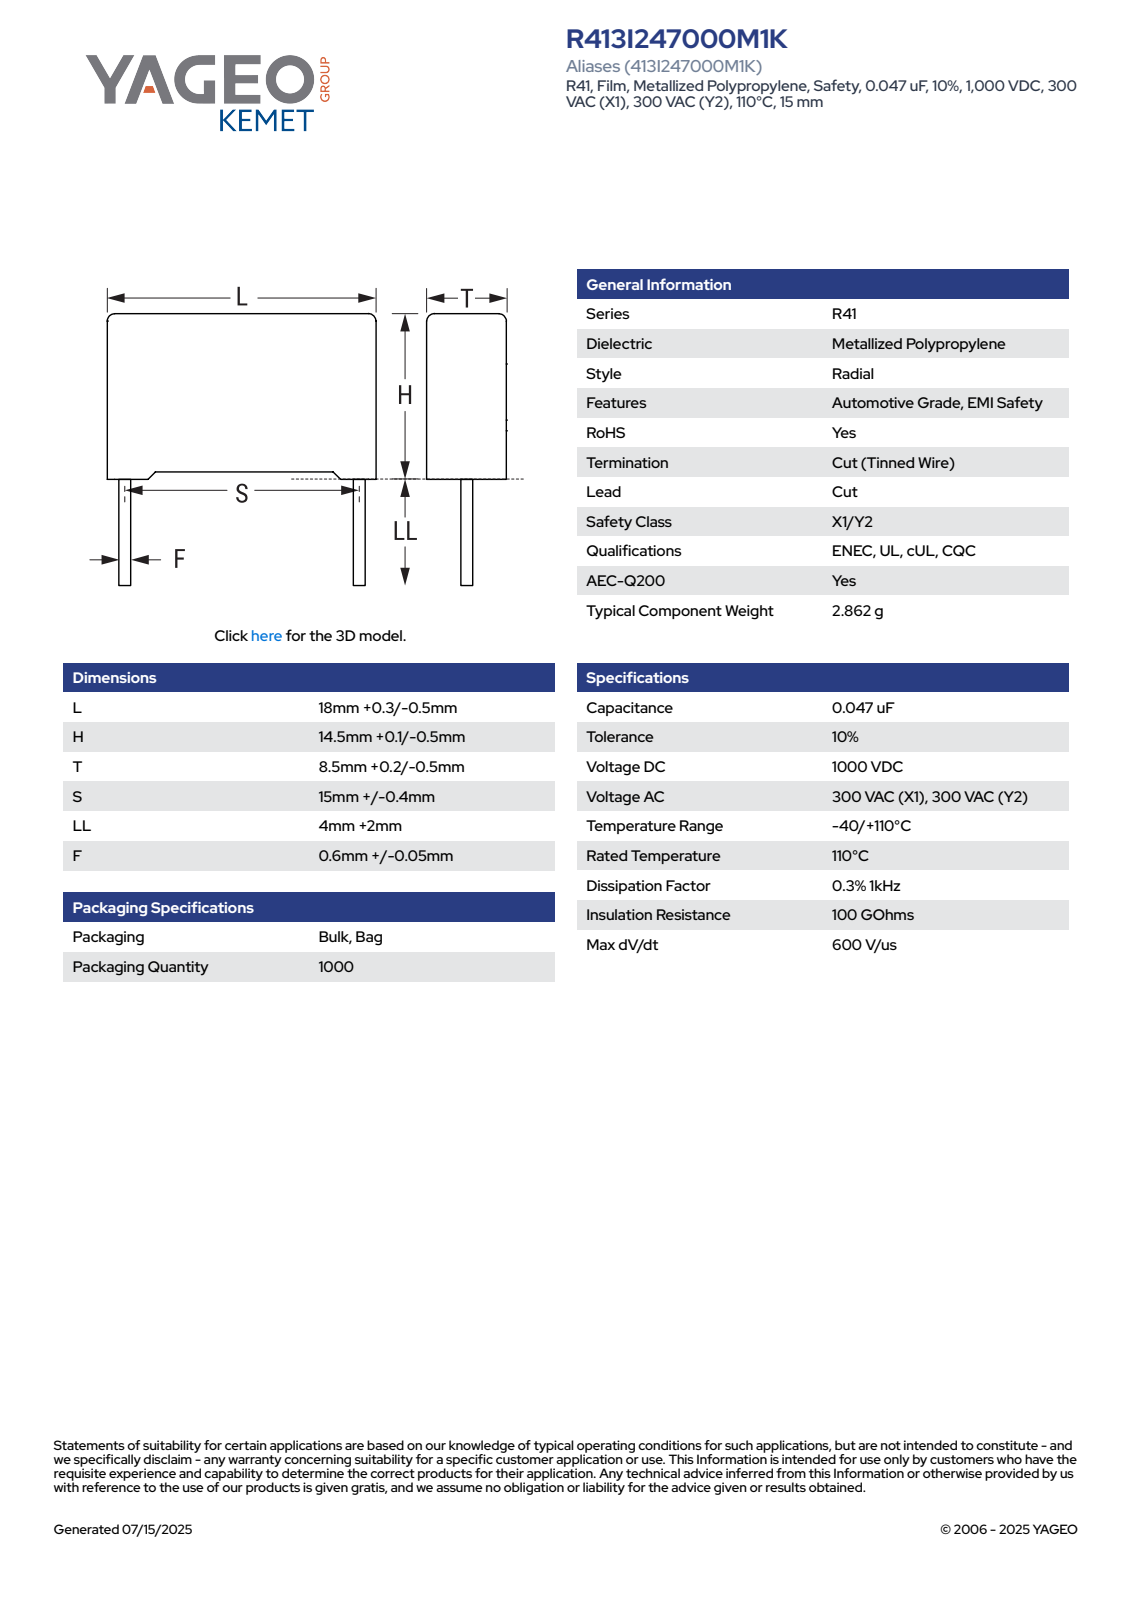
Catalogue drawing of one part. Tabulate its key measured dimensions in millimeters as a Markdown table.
| quantity | value |
| --- | --- |
| part name | CFR_RB2_18X14.5X8.5_L18.3H14.6T8.7S15LL6F0.65 |
| STEP written by | SolidWorks 2021 (AUTOMOTIVE_DESIGN) |
| units | millimeters |
| bodies | 4 solids, 85 faces (77 planar, 8 cylindrical, 0 other) |
| overall size | 20.6 × 18.3 × 8.71 |
| volume | 2 223 mm³ |
| surface area | 1 162 mm² |
| round bosses / shafts (diameter × count) | 0.65 × 2 |
| partial cylindrical surfaces (radius × count) | 0.5 × 4 |
| main face-to-face distances | 8.7, 13.85, 18.3, 0.61, 0.75, 14.6, 8.09, 0.5, 14.1, 17.69 |
